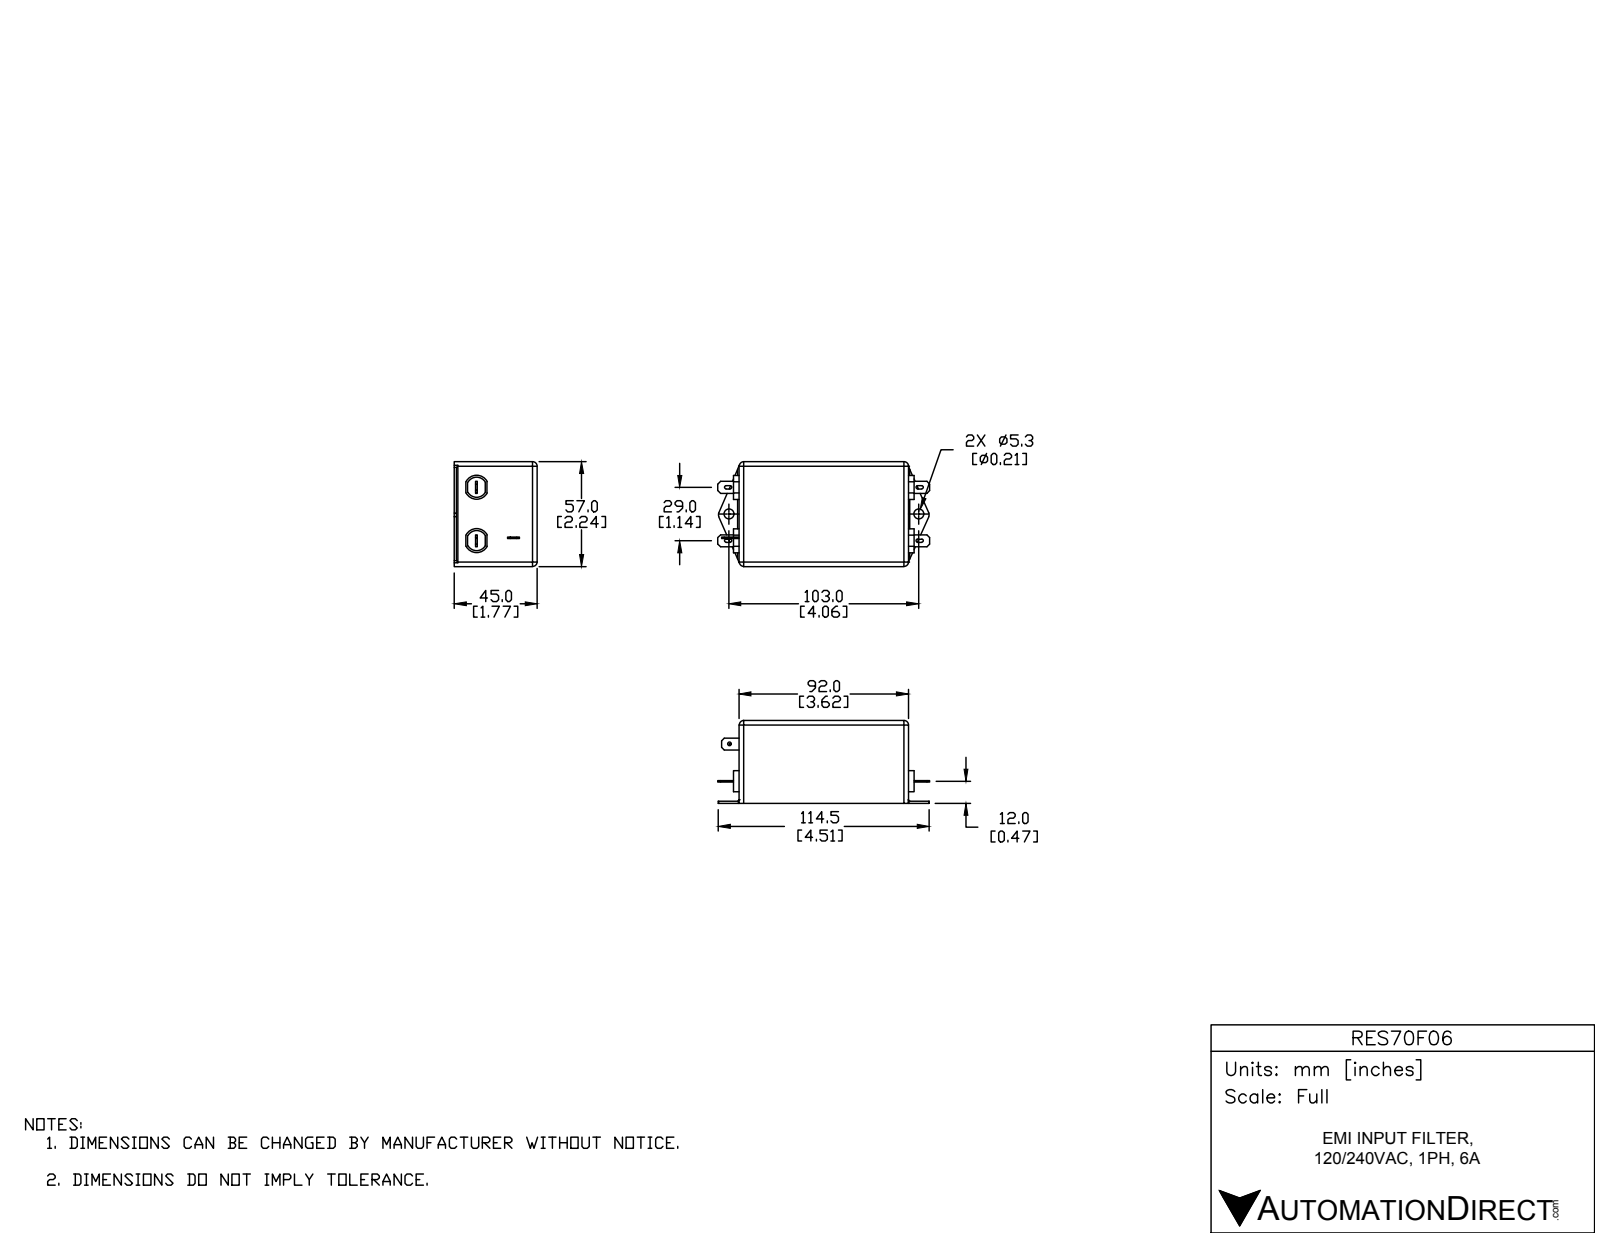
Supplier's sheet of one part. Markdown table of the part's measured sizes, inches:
| quantity | value |
| --- | --- |
| part name | RES70F06 |
| STEP written by | SolidWorks 2015 (AUTOMOTIVE_DESIGN) |
| units | inches |
| bodies | 1 solid, 133 faces (79 planar, 50 cylindrical, 4 other) |
| overall size | 4.528 × 2.244 × 1.772 |
| volume | 14.48 in³ |
| surface area | 40.09 in² |
| round holes (diameter × count) | 0.209 × 2, 0.079 × 1 |
| partial cylindrical surfaces (radius × count) | 0.098 × 10, 0.035 × 8, 0.03 × 2, 0.217 × 2, 0.256 × 2 |
| main face-to-face distances | 1.772, 2.244, 3.622, 0.059, 0.047, 1.724, 3.681, 3.74, 0.031, 0.457 |
| hole center spacings | 4.055 |
